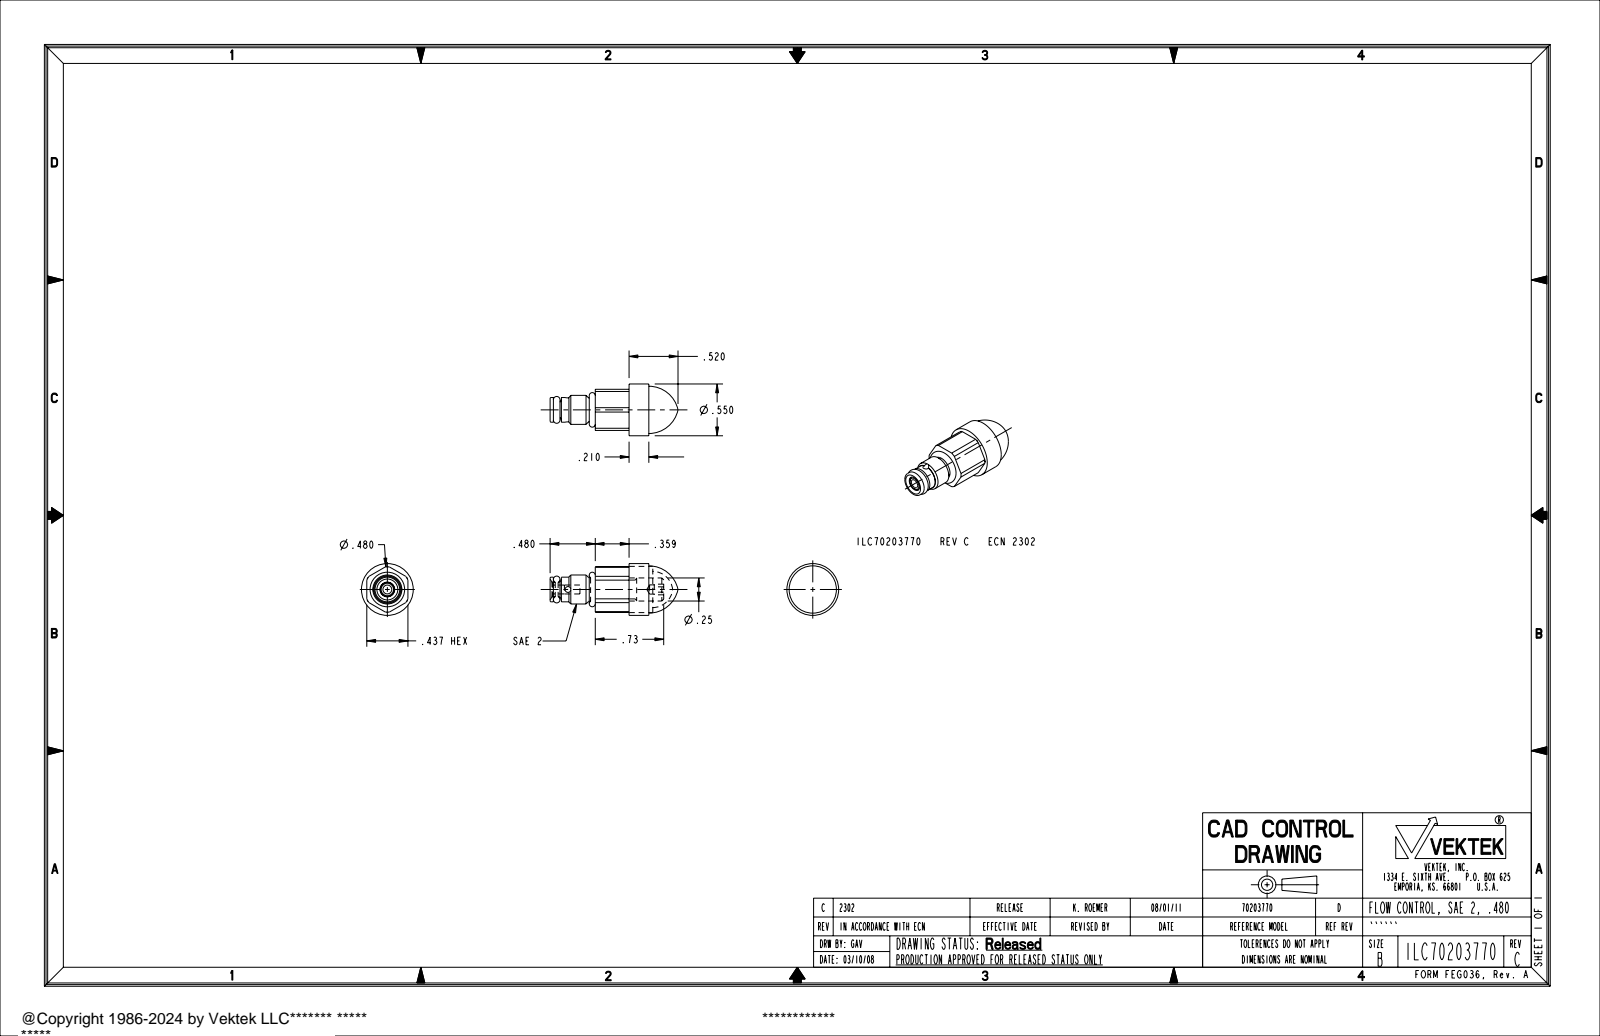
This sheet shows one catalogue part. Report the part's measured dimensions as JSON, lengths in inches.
{"part_name": "ILC70203770", "step_written_by": "PRO/ENGINEER BY PARAMETRIC TECHNOLOGY CORPORATION, 2007460 (AUTOMOTIVE_DESIGN_CC2)", "units": "inches", "bodies": {"solids": 2, "faces": 104, "planar": 38, "cylindrical": 36, "other": 30}, "overall_size": [1.359, 0.55, 0.55], "volume_in3": 0.135, "surface_area_in2": 3.541, "round_holes": [[0.062, 1], [0.094, 1], [0.095, 1], [0.098, 1], [0.156, 1]], "round_bosses_or_shafts": [[0.55, 1], [0.308, 1], [0.262, 1], [0.25, 1], [0.245, 1], [0.2, 1], [0.152, 1]], "partial_cylinders_radius": [[0.24, 1]], "face_to_face_distances": [0.431, 0.437, 0.425, 0.359, 0.252, 0.611, 0.042, 0.21, 0.569, 1.056]}
